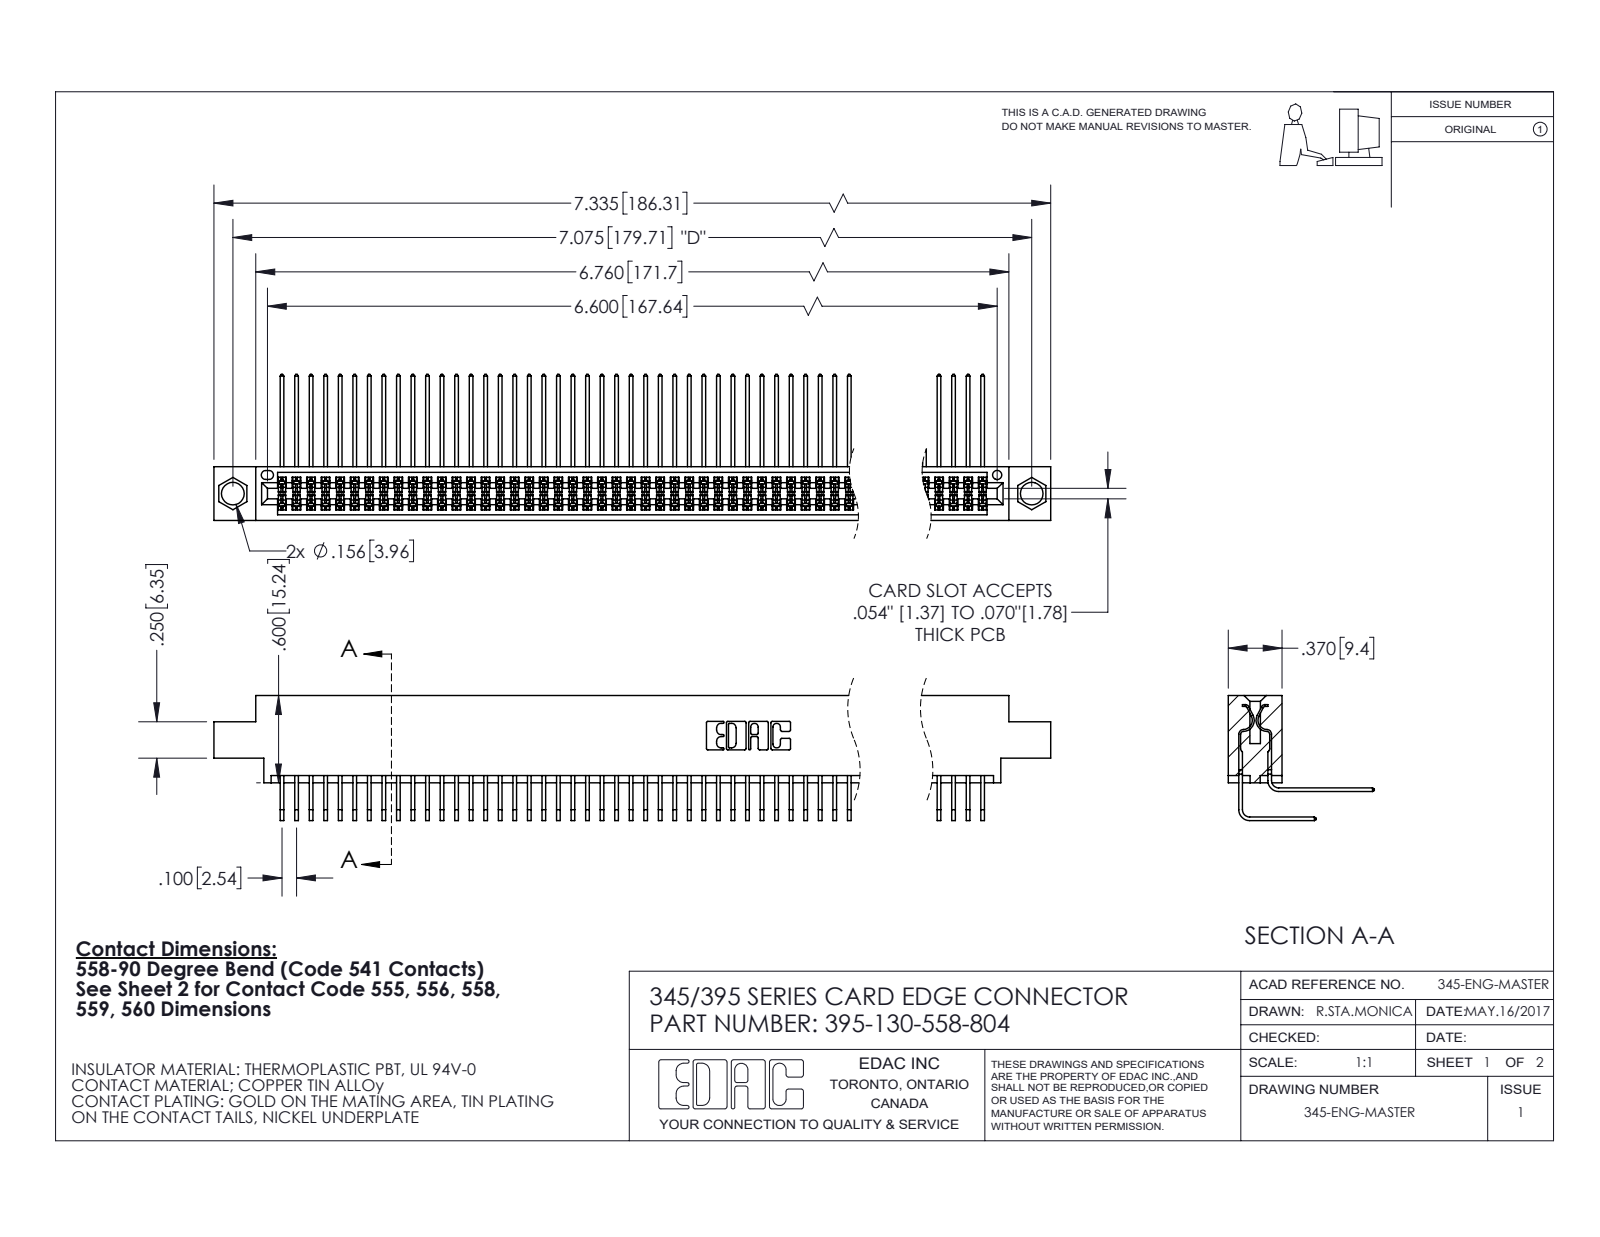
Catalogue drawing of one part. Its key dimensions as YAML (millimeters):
part_name: "345-292-001_558 559 Tail - 1; 345-292-001_558 Tail - 2; 395-130-558-804; 345 Part_0.170 Offset - 0.156 Dia-TI"
step_written_by: "SolidWorks 2020 (CONFIG_CONTROL_DESIGN)"
units: millimeters
bodies: {solids: 131, faces: 6904, planar: 4648, cylindrical: 2256, other: 0}
overall_size: [186.3, 25.5, 21.8]
volume: 18850
surface_area: 31820
round_holes:
  - {diameter: 4, count: 2}
  - {diameter: 1.6, count: 1}
partial_cylinders:
  - {radius: 0.2, count: 195}
  - {radius: 0.3, count: 22}
  - {radius: 0.2, count: 6}
  - {radius: 0.8, count: 6}
  - {radius: 0.7, count: 3}
  - {radius: 0.4, count: 2}
  - {radius: 0.5, count: 2}
  - {radius: 0.6, count: 2}
face_to_face_distances: [1.8, 7.6, 5.1, 9.4, 2.5, 6.9, 0.6, 5.7, 4.4, 0.6]
hole_center_spacings: [6.9, 173.7, 179.7]
